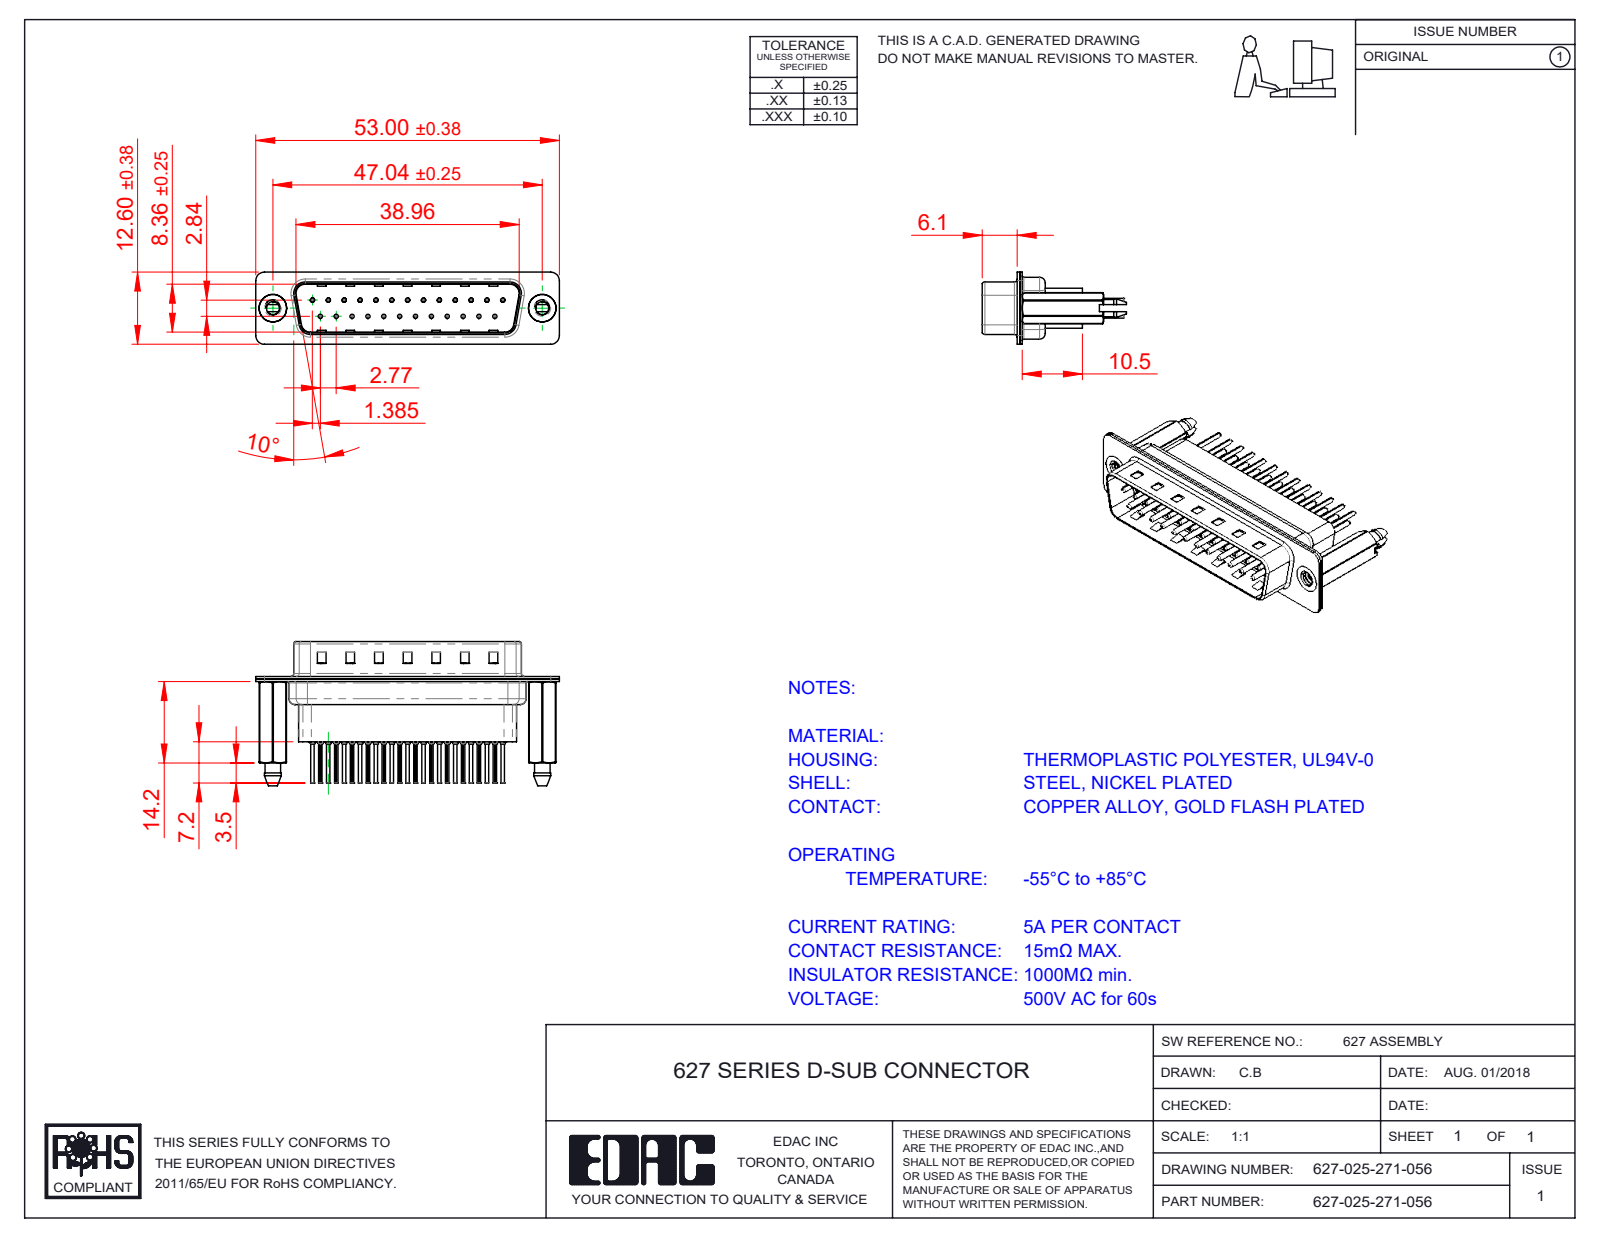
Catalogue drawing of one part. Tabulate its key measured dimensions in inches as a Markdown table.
| quantity | value |
| --- | --- |
| part name | 627 Contact Row 1_61; 627 Shell Front_25 Contacts; 627 4-40 Threaded Boardlock_HP71; 627-025-271-056 (+3 more) |
| STEP written by | SolidWorks 2020 (CONFIG_CONTROL_DESIGN) |
| units | inches |
| bodies | 30 solids, 2934 faces (803 planar, 1128 cylindrical, 1003 other) |
| overall size | 2.087 × 0.988 × 0.496 |
| volume | 0.255 in³ |
| surface area | 16.73 in² |
| round holes (diameter × count) | 0.008 × 25, 0.014 × 25, 0.043 × 25, 0.063 × 25, 0.089 × 2, 0.157 × 2, 0.189 × 2 |
| round bosses / shafts (diameter × count) | 0.079 × 25, 0.059 × 25, 0.03 × 25, 0.024 × 25, 0.193 × 2 |
| partial cylindrical surfaces (radius × count) | 0.004 × 50, 0.059 × 18, 0.079 × 12, 0.063 × 10, 0.02 × 8, 0.01 × 4, 0.024 × 4, 0.026 × 4 |
| main face-to-face distances | 0.016, 0.018, 0.032, 0.377, 0.027, 0.302, 0.059, 0.035, 0.043, 0.318 |
| hole center spacings | 0.124, 0.327, 0.109, 0.218, 0.436, 0.654, 0.198, 0.198 |
